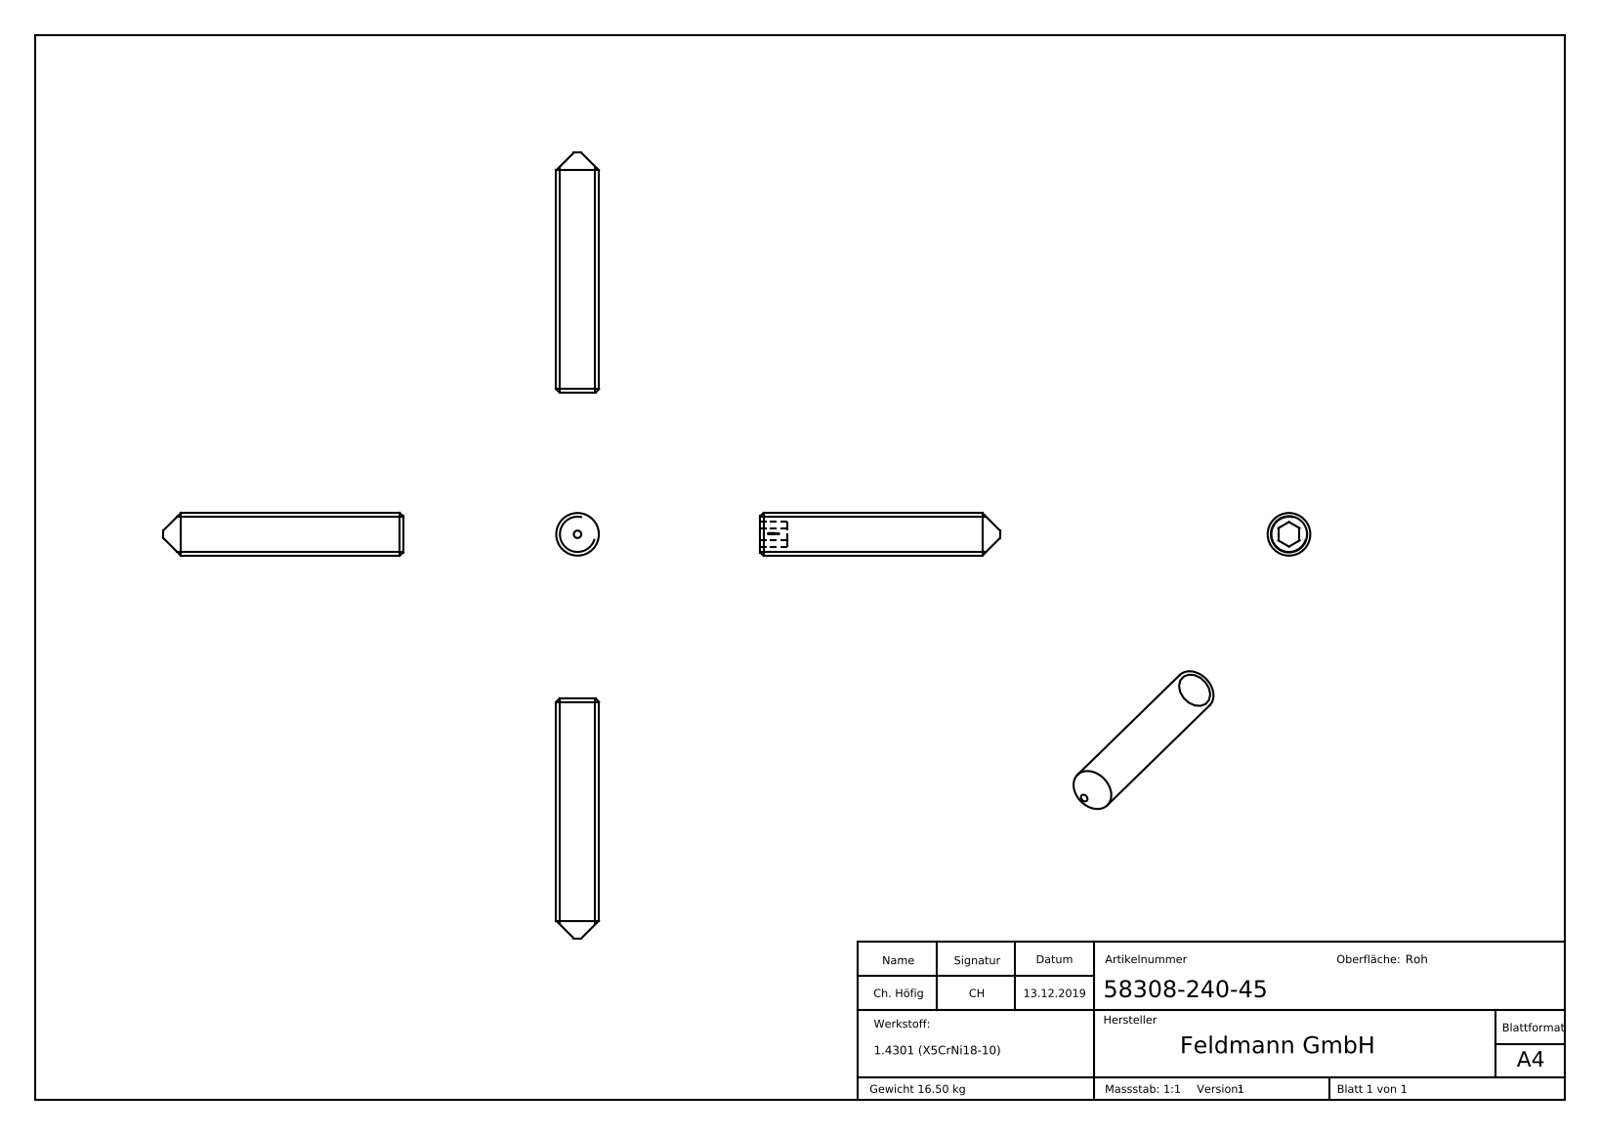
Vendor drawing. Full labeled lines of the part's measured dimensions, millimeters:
Part name (STEP PRODUCT): 58308-240-45
STEP written by: SolidWorks 2015 (CONFIG_CONTROL_DESIGN)
Units: millimetres
Bodies: 1 solid, 182 faces (86 planar, 1 cylindrical, 95 other)
Overall size (bounding box): 70 × 8 × 8
Volume: 2 089 mm³ · Surface area: 1 230 mm²
Round bosses / shafts (diameter × count): ⌀8 ×1
Main face-to-face distances: 4, 5, 40, 45, 4.1, 0.41, 0.51, 1.64, 41.64, 42.15
